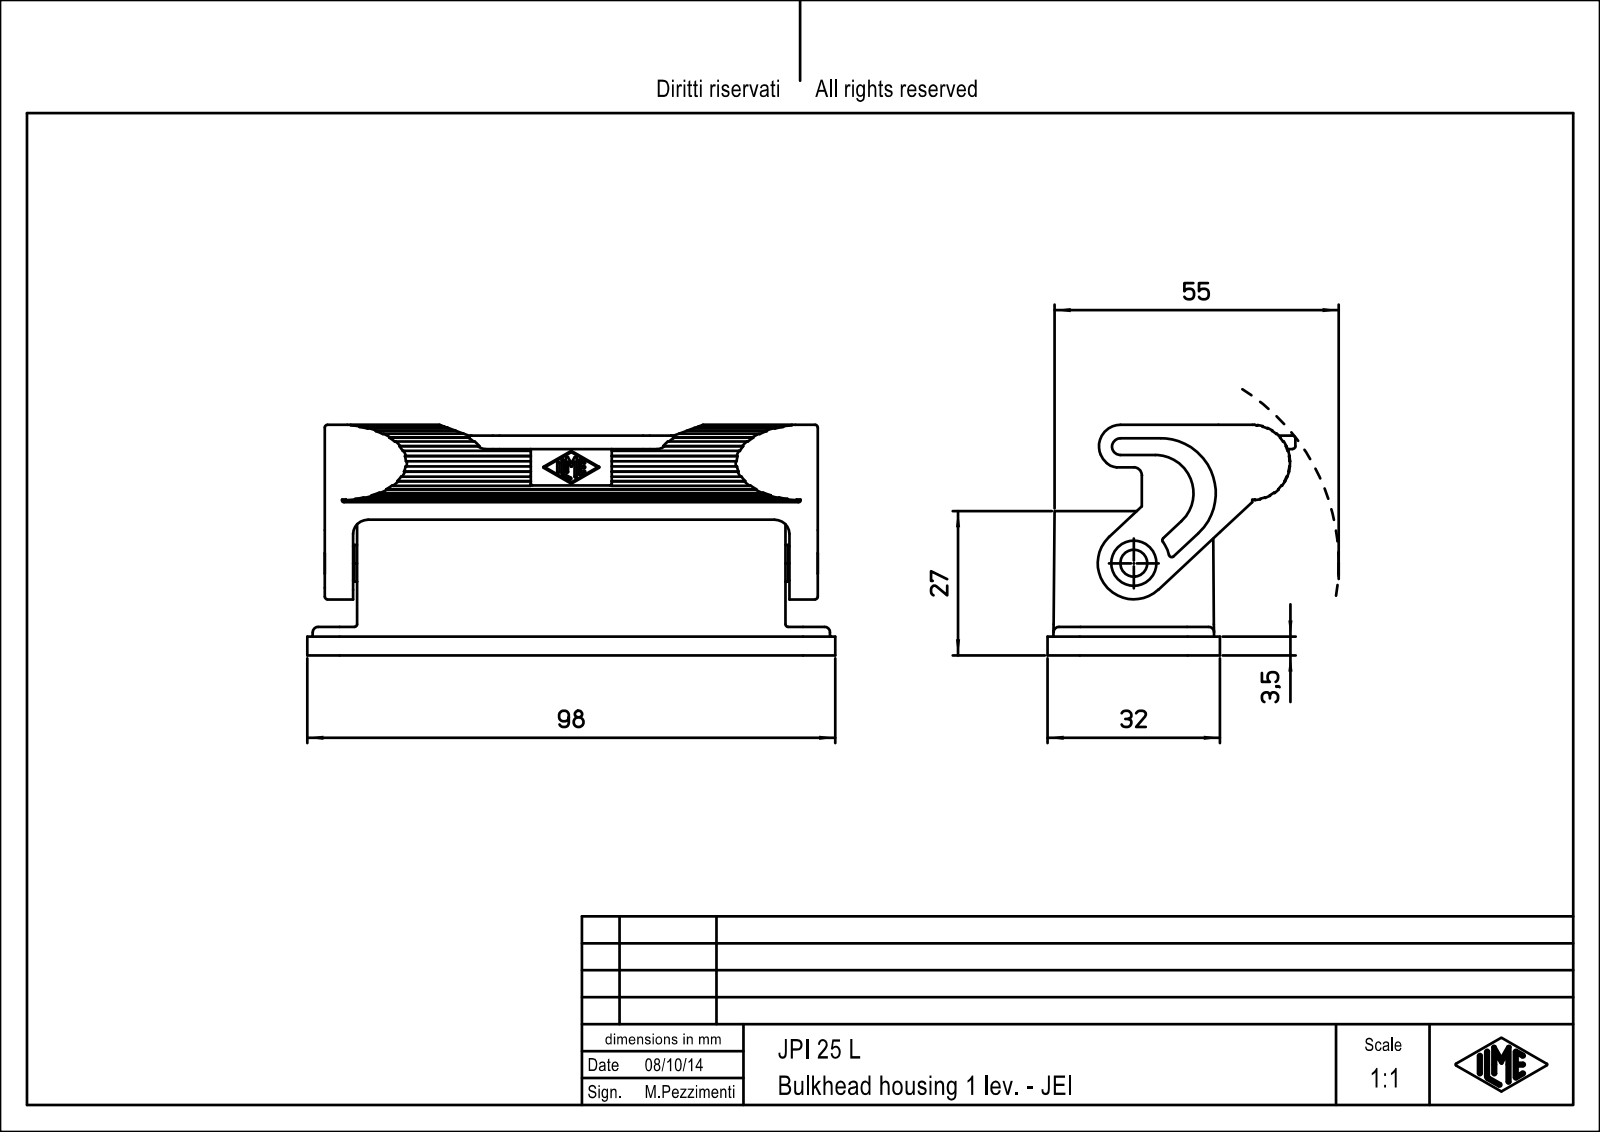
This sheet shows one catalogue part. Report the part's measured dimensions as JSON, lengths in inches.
{"part_name": "CZI.SUPP.SPORT_25.1; LEVA_JP25; JPI_25_L", "step_written_by": "Creo Elements/Direct Modeling 18.1F 24-Jul-2014 (C) Parametric Technology GmbH (AUTOMOTIVE_DESIGN)", "units": "inches", "bodies": {"solids": 2, "faces": 441, "planar": 162, "cylindrical": 213, "other": 66}, "overall_size": [3.858, 1.811, 1.685], "volume_in3": 2.225, "surface_area_in2": 35.36, "round_holes": [[0.11, 4], [0.118, 4], [0.134, 4], [0.128, 1], [0.197, 1], [0.331, 1]], "round_bosses_or_shafts": [[0.268, 1], [0.189, 1], [0.126, 1]], "partial_cylinders_radius": [[0.02, 38], [0.008, 15], [0.138, 8], [0.118, 7], [0.039, 4], [0.098, 4], [0.197, 4], [0.236, 4]], "face_to_face_distances": [0.138, 0.207, 3.396, 3.189, 1.055, 0.203, 1.057, 0.209, 0.551, 1.26], "hole_center_spacings": [0.395, 0.768, 2.992, 3.064, 0.63, 0.689, 2.598, 2.674]}
